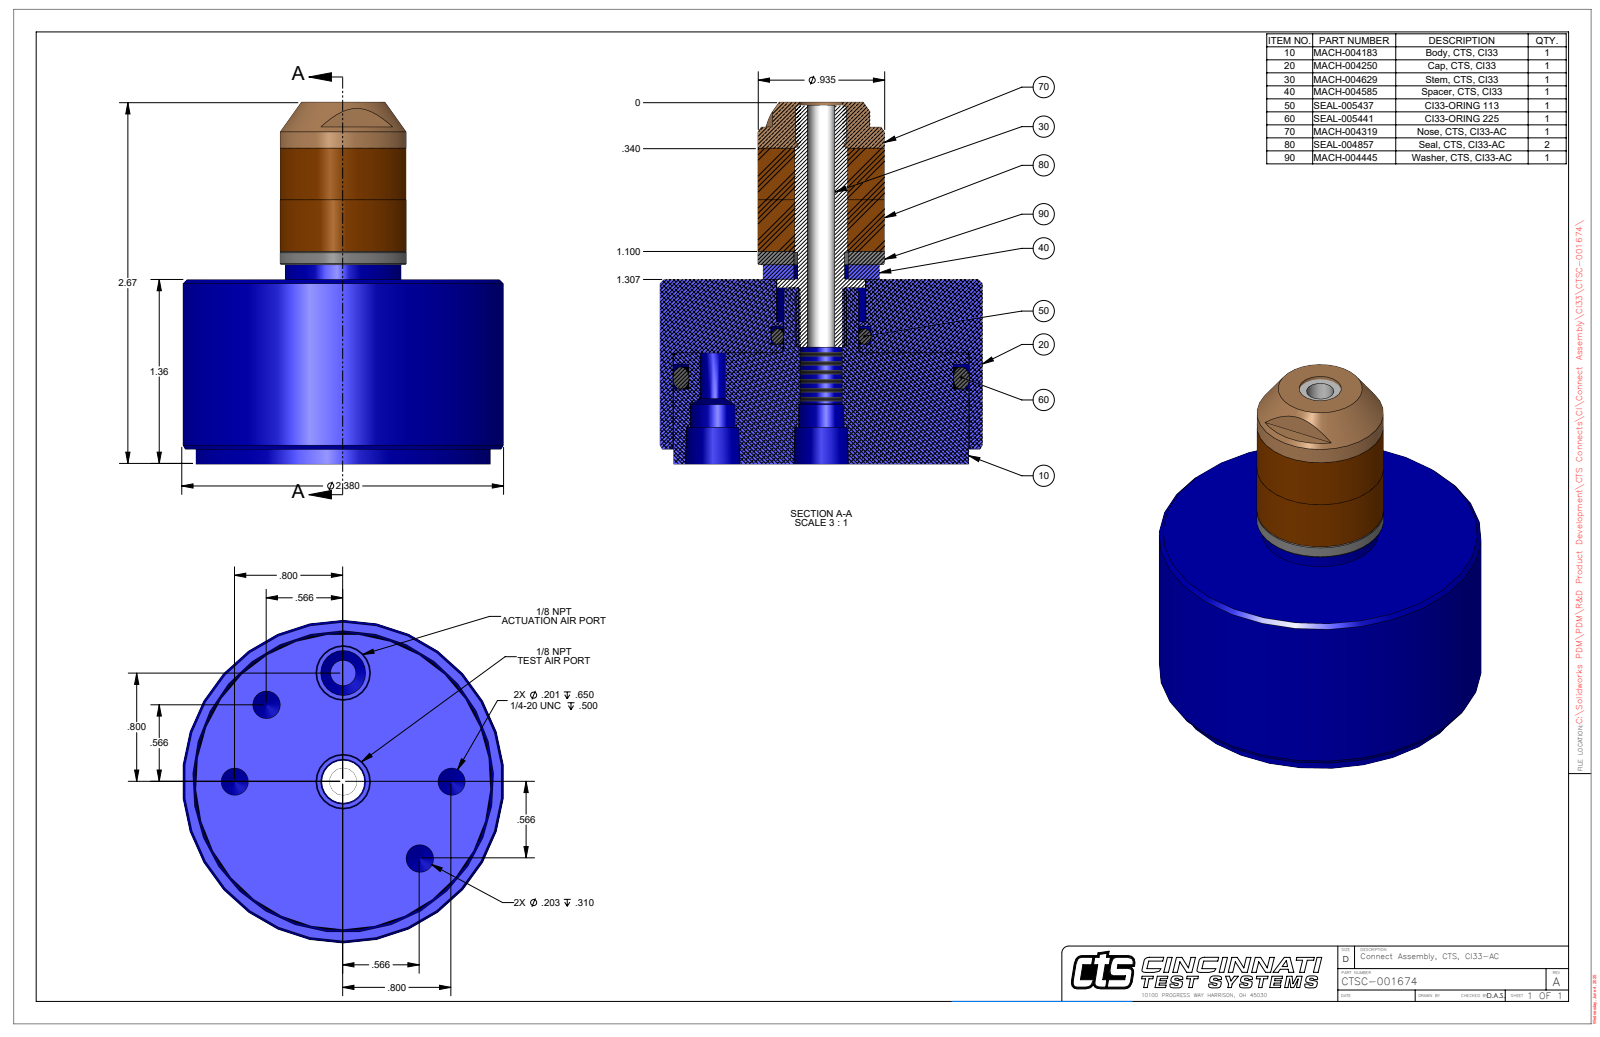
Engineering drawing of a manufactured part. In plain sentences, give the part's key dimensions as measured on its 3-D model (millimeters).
The part is named "CTSC-001674". Its 3-D file was written by "SolidWorks 2023 (AUTOMOTIVE_DESIGN)". It is 1 solid with 76 faces: 20 planar, 32 cylindrical and 24 other. Overall it measures 67.7 by 60.5 by 60.5 millimeters. Its volume is 107 600 cubic millimeters and its surface area 19 650 square millimeters. Round holes: 2 of diameter 5.1, 2 of diameter 5.2, 2 of diameter 8.4, 1 of diameter 5.2, 1 of diameter 8, 1 of diameter 16.7, 1 of diameter 55.6. Round bosses or shafts: 1 of diameter 60.5, 1 of diameter 55.3, 1 of diameter 23.7, 1 of diameter 21.8, 1 of diameter 16.5. The main face-to-face distances are 34.5, 2.8, 31.8, 67.7, 64.9, 33.2, 11.3, 8.5, 23.2, 56.4. The hole center spacings are 20.3, 15.5, 37.5, 28.7, 40.6.
